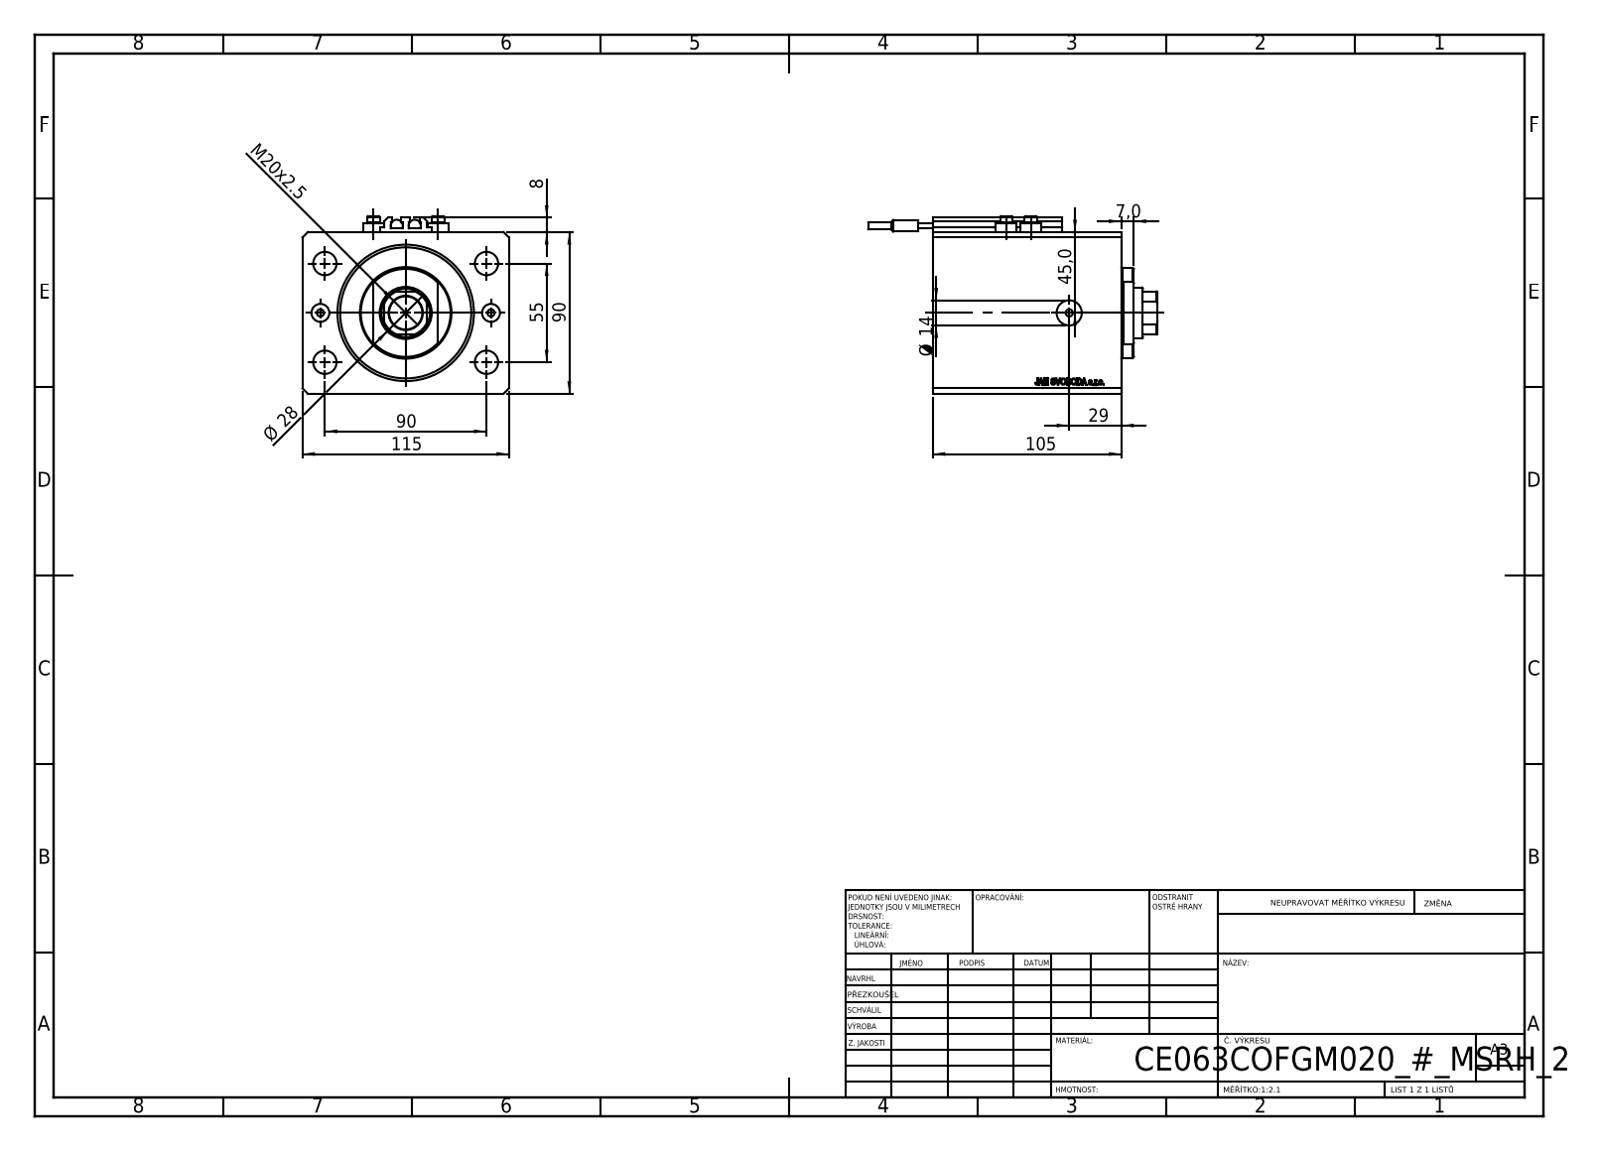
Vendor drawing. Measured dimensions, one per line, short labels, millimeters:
name: ALLEN BOLT V250CE; V250CE_C_Body; V250CE_C_VCP; SWITCH_V250CE (+1 more)
written by: SolidWorks 2019 (CONFIG_CONTROL_DESIGN)
unit: mm
bodies: 10 solids, 1086 faces (536 planar, 98 cylindrical, 452 other)
size: 161 × 115 × 99
volume: 1 000 000 mm³; area: 150 411 mm²
holes: 8× ⌀4, 4× ⌀13, 2× ⌀10, 2× ⌀14, 1× ⌀18.5, 1× ⌀28, 1× ⌀63, 1× ⌀76
bosses: 4× ⌀11.6, 4× ⌀7, 2× ⌀6.8, 2× ⌀6.5, 2× ⌀4, 1× ⌀50
rounds: 10× R0.2, 1× R13.5
face distances: 90, 115, 20, 105, 17.9, 87.1, 85, 67.1, 40, 65
hole spacings: 27.61, 52.74, 96.5, 13.6, 36, 38.48, 47.5, 55
